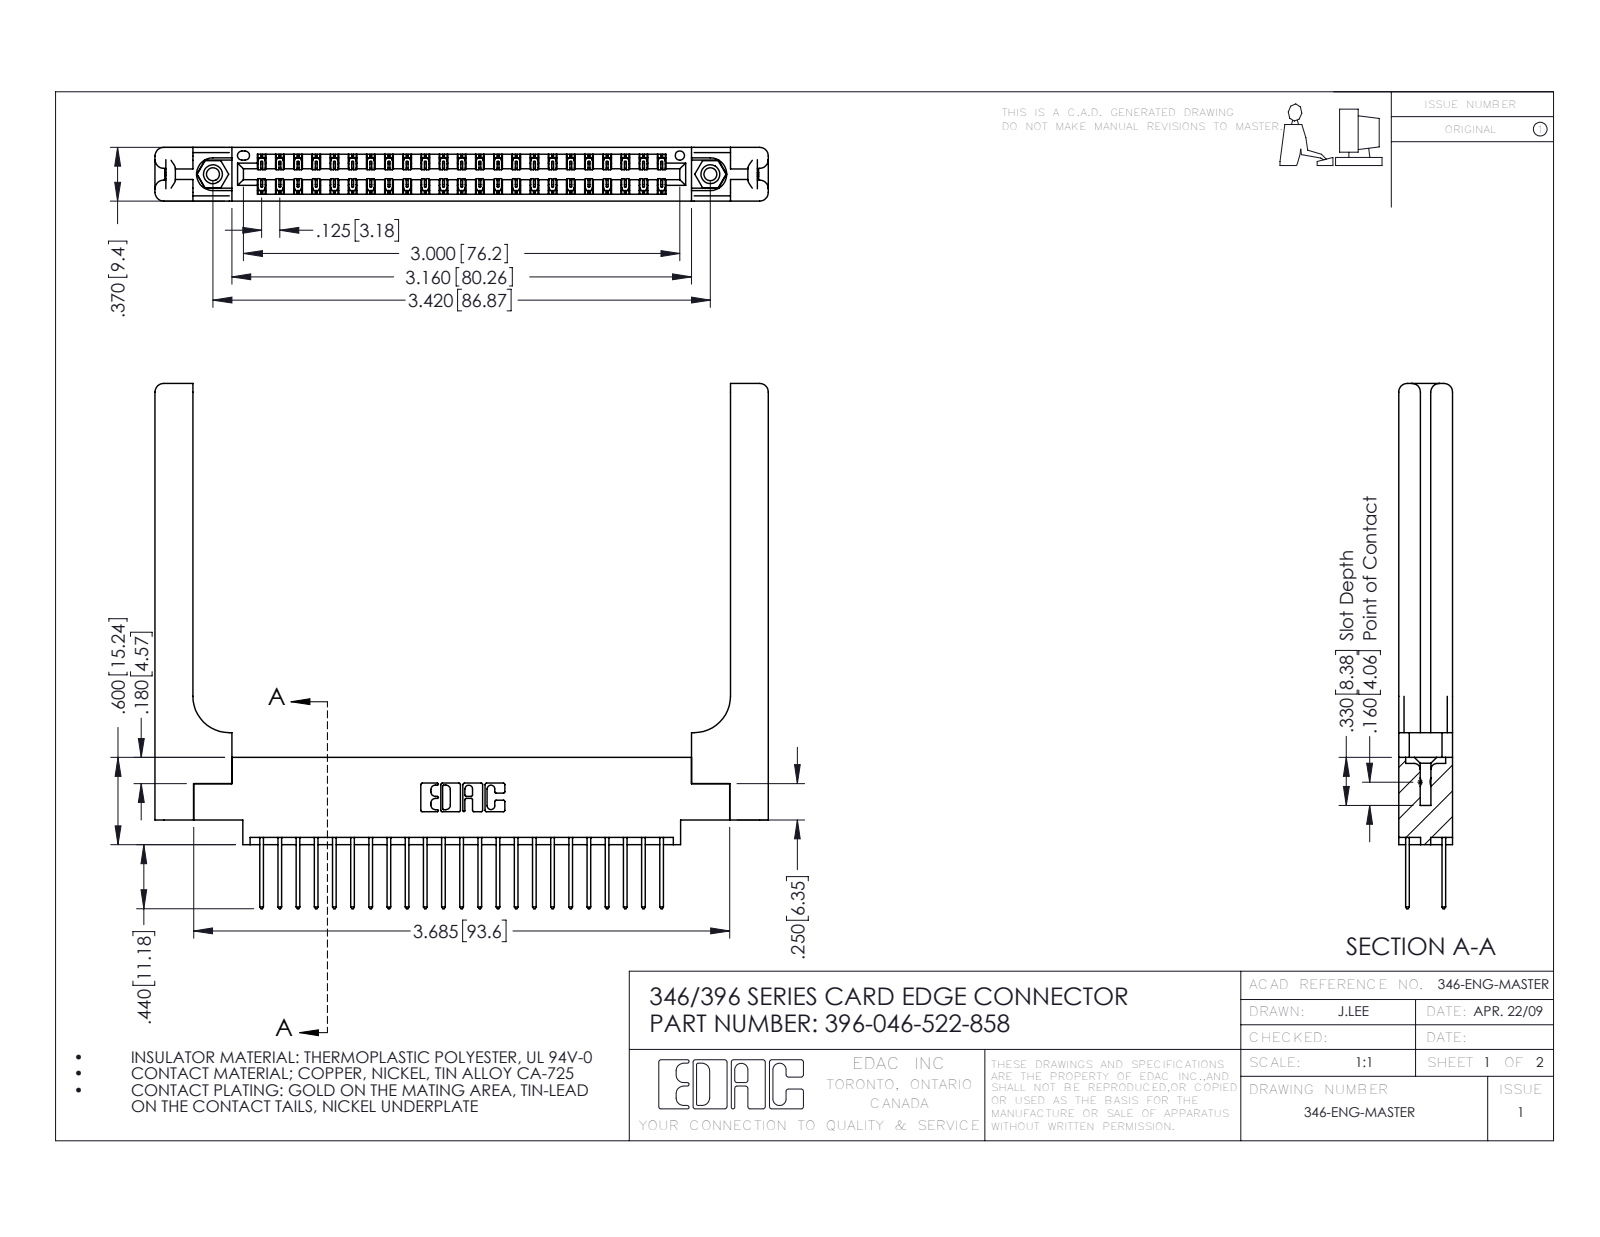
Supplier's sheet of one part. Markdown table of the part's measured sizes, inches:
| quantity | value |
| --- | --- |
| part name | 346 Part_0.170 Offset - 0.156 Dia-TH; 396-046-522-858; 345-250-001_345-250-001-102; 345-292-001_345-293-122 (+1 more) |
| STEP written by | SolidWorks 2016 (CONFIG_CONTROL_DESIGN) |
| units | inches |
| bodies | 51 solids, 2774 faces (1838 planar, 876 cylindrical, 60 other) |
| overall size | 4.216 × 3.61 × 0.37 |
| volume | 1.083 in³ |
| surface area | 30.23 in² |
| round holes (diameter × count) | 0.089 × 2, 0.125 × 2, 0.156 × 2, 0.064 × 1 |
| round bosses / shafts (diameter × count) | 0.155 × 2 |
| partial cylindrical surfaces (radius × count) | 0.006 × 69, 0.01 × 46, 0.01 × 22, 0.06 × 16, 0.007 × 6, 0.031 × 6, 0.026 × 3, 0.014 × 2 |
| main face-to-face distances | 0.37, 0.072, 0.048, 0.322, 0.148, 0.15, 0.25, 0.025, 0.298, 0.275 |
| hole center spacings | 0.246, 3.212, 3.42 |
